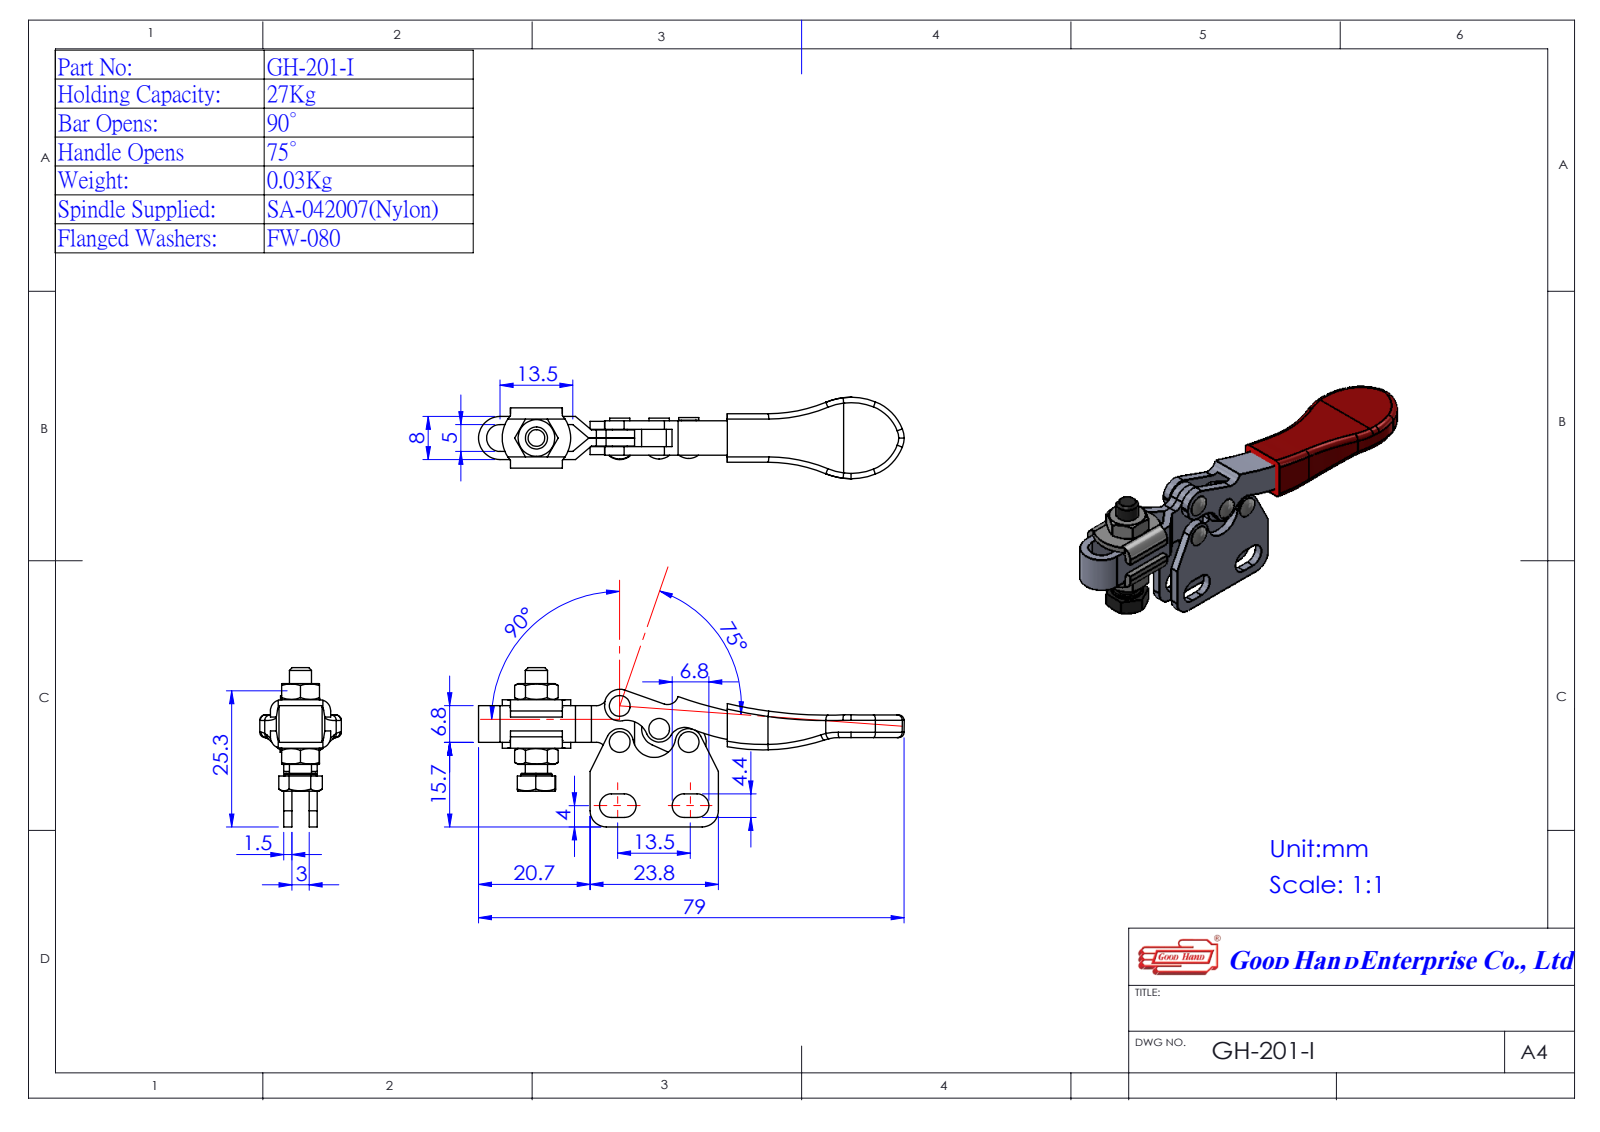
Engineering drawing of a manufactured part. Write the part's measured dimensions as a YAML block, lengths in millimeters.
part_name: "120108-1-1^GH-201-I(簡化)-1; 120105-1^GH-201-I(簡化)-1; GH-201-I(簡化)-1; Group1^GH-201-I(簡化)-1 (+2 more)"
step_written_by: "SolidWorks 2016 (AUTOMOTIVE_DESIGN)"
units: millimeters
bodies: {solids: 7, faces: 286, planar: 125, cylindrical: 153, other: 8}
overall_size: [79, 31.15, 15.02]
volume: 2721
surface_area: 7186
round_holes:
  - {diameter: 2.5, count: 4}
round_bosses_or_shafts:
  - {diameter: 3.75, count: 4}
  - {diameter: 2.75, count: 2}
  - {diameter: 5.8, count: 1}
  - {diameter: 4.1, count: 1}
partial_cylinders:
  - {radius: 1, count: 6}
  - {radius: 4, count: 5}
  - {radius: 2.1, count: 4}
  - {radius: 2.2, count: 4}
  - {radius: 2.5, count: 4}
  - {radius: 2.8, count: 3}
  - {radius: 3.25, count: 2}
  - {radius: 5.26, count: 2}
face_to_face_distances: [1.5, 1.6, 3.2, 4.9, 6.4, 4.8, 1.7, 1.26, 3.3, 0.8]
hole_center_spacings: [6, 6.7, 7.72, 8.46, 12.8, 14.45]
